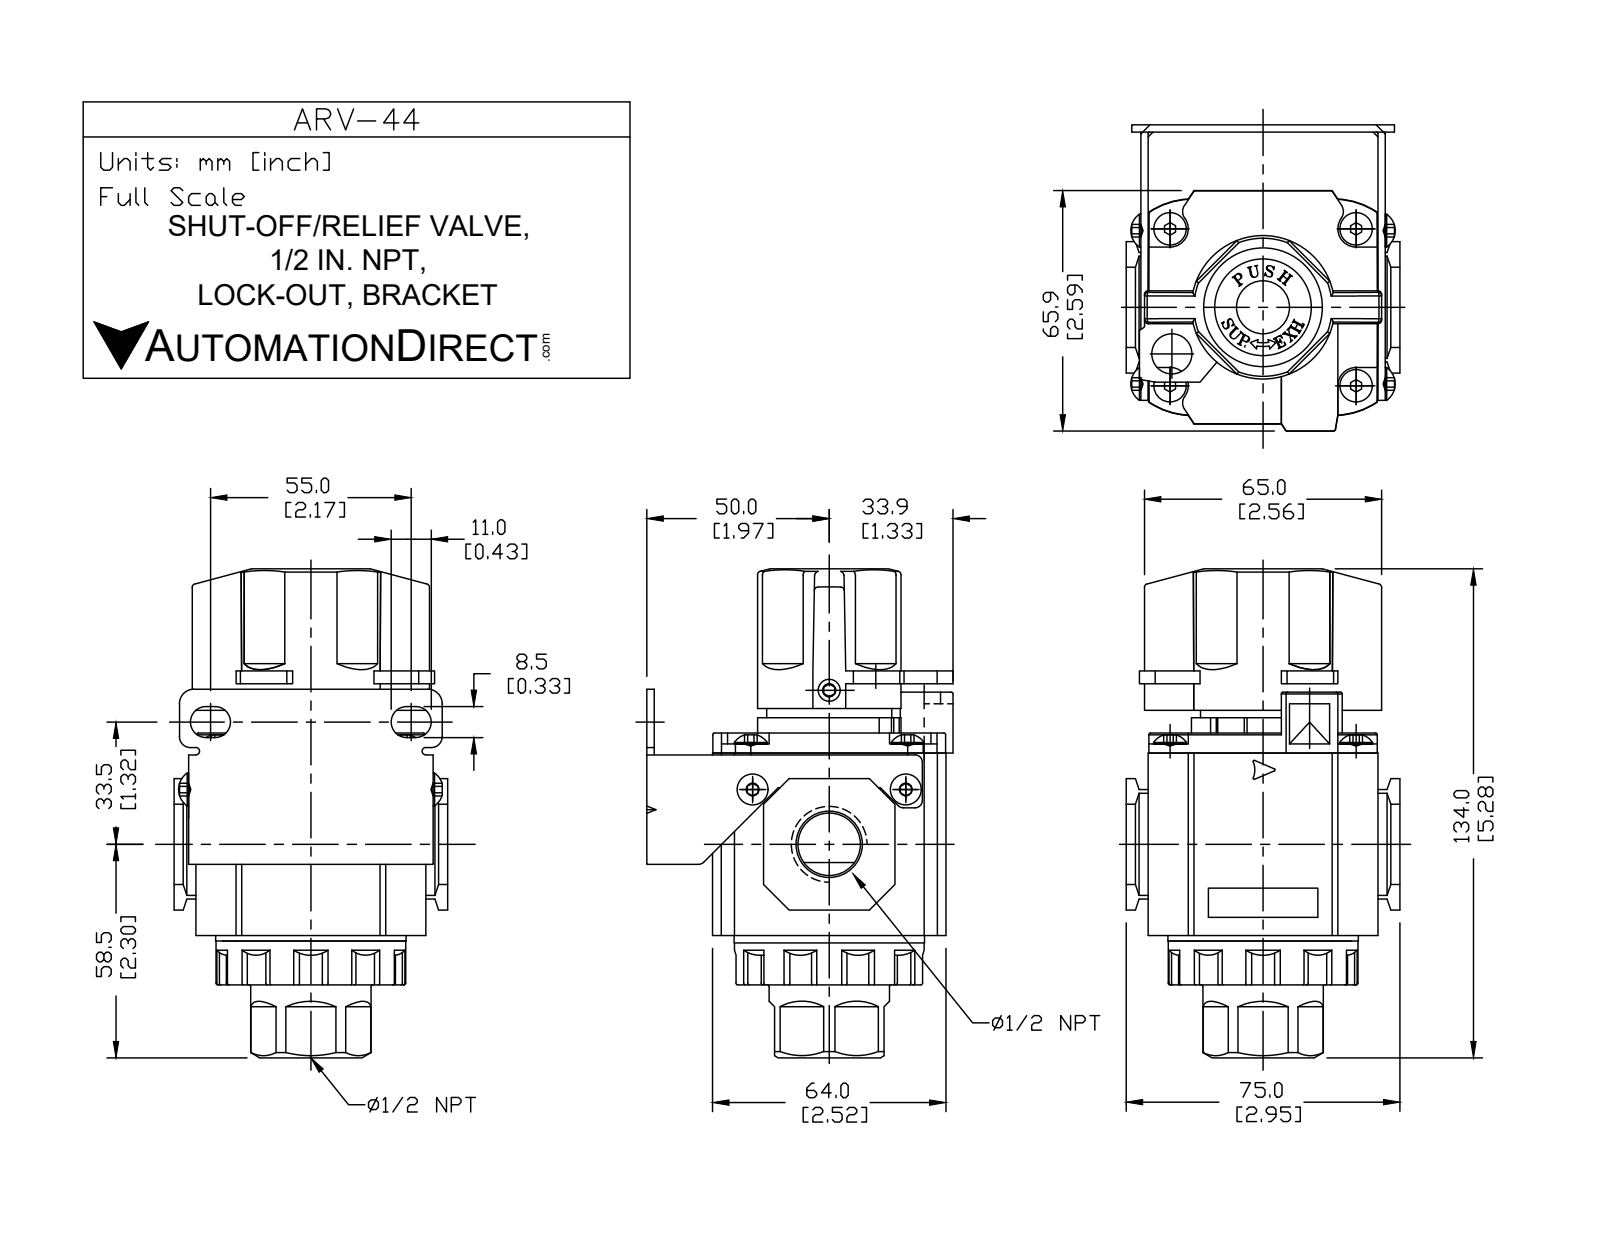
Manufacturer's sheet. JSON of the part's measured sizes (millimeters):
{"part_name": "ARV-44", "step_written_by": "SolidWorks 2015 (CONFIG_CONTROL_DESIGN)", "units": "millimeters", "bodies": {"solids": 18, "faces": 421, "planar": 292, "cylindrical": 83, "other": 46}, "overall_size": [134, 84, 75], "volume_mm3": 331047, "surface_area_mm2": 71673, "round_holes": [[11, 1], [17.86, 1], [27.51, 1]], "round_bosses_or_shafts": [[9, 4], [8.5, 2], [52, 1], [50.96, 1], [39.3, 1], [33, 1], [19.65, 1]], "partial_cylinders_radius": [[1.5, 6], [4.25, 4], [6.3, 4], [1, 2], [2, 2], [3, 2], [5, 1], [16.2, 1]], "face_to_face_distances": [2, 50, 4.85, 54.85, 63, 65, 64, 18, 82, 16], "hole_center_spacings": [28.06]}
